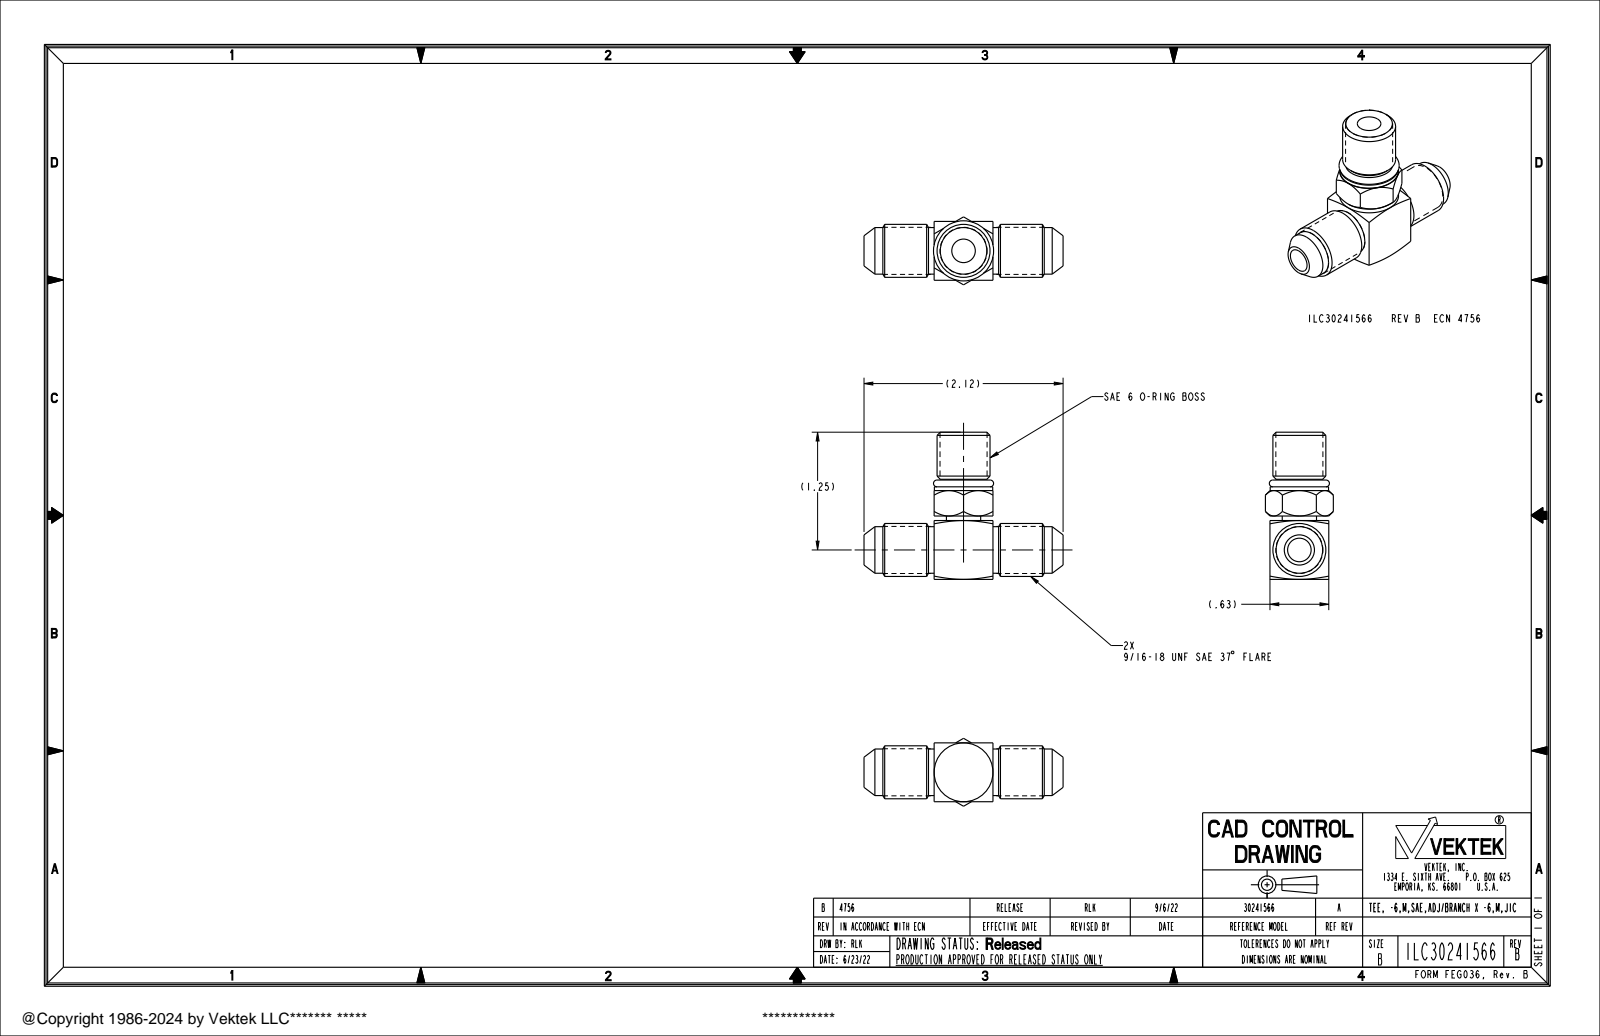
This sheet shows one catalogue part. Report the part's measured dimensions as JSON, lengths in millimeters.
{"part_name": "ILC30241566", "step_written_by": "CREO PARAMETRIC BY PTC INC, 2021164 (AUTOMOTIVE_DESIGN)", "units": "millimeters", "bodies": {"solids": 2, "faces": 90, "planar": 18, "cylindrical": 30, "other": 42}, "overall_size": [53.7, 39.7, 18.3], "volume_mm3": 10800, "surface_area_mm2": 7935, "round_holes": [[6.4, 2]], "round_bosses_or_shafts": [[14.3, 2], [12.7, 2], [12.5, 2], [15.7, 1], [9.2, 1]], "face_to_face_distances": [15.9, 17.1, 1.2, 39.7, 23.8, 22.6, 25, 9.1, 7.9, 14.7]}
